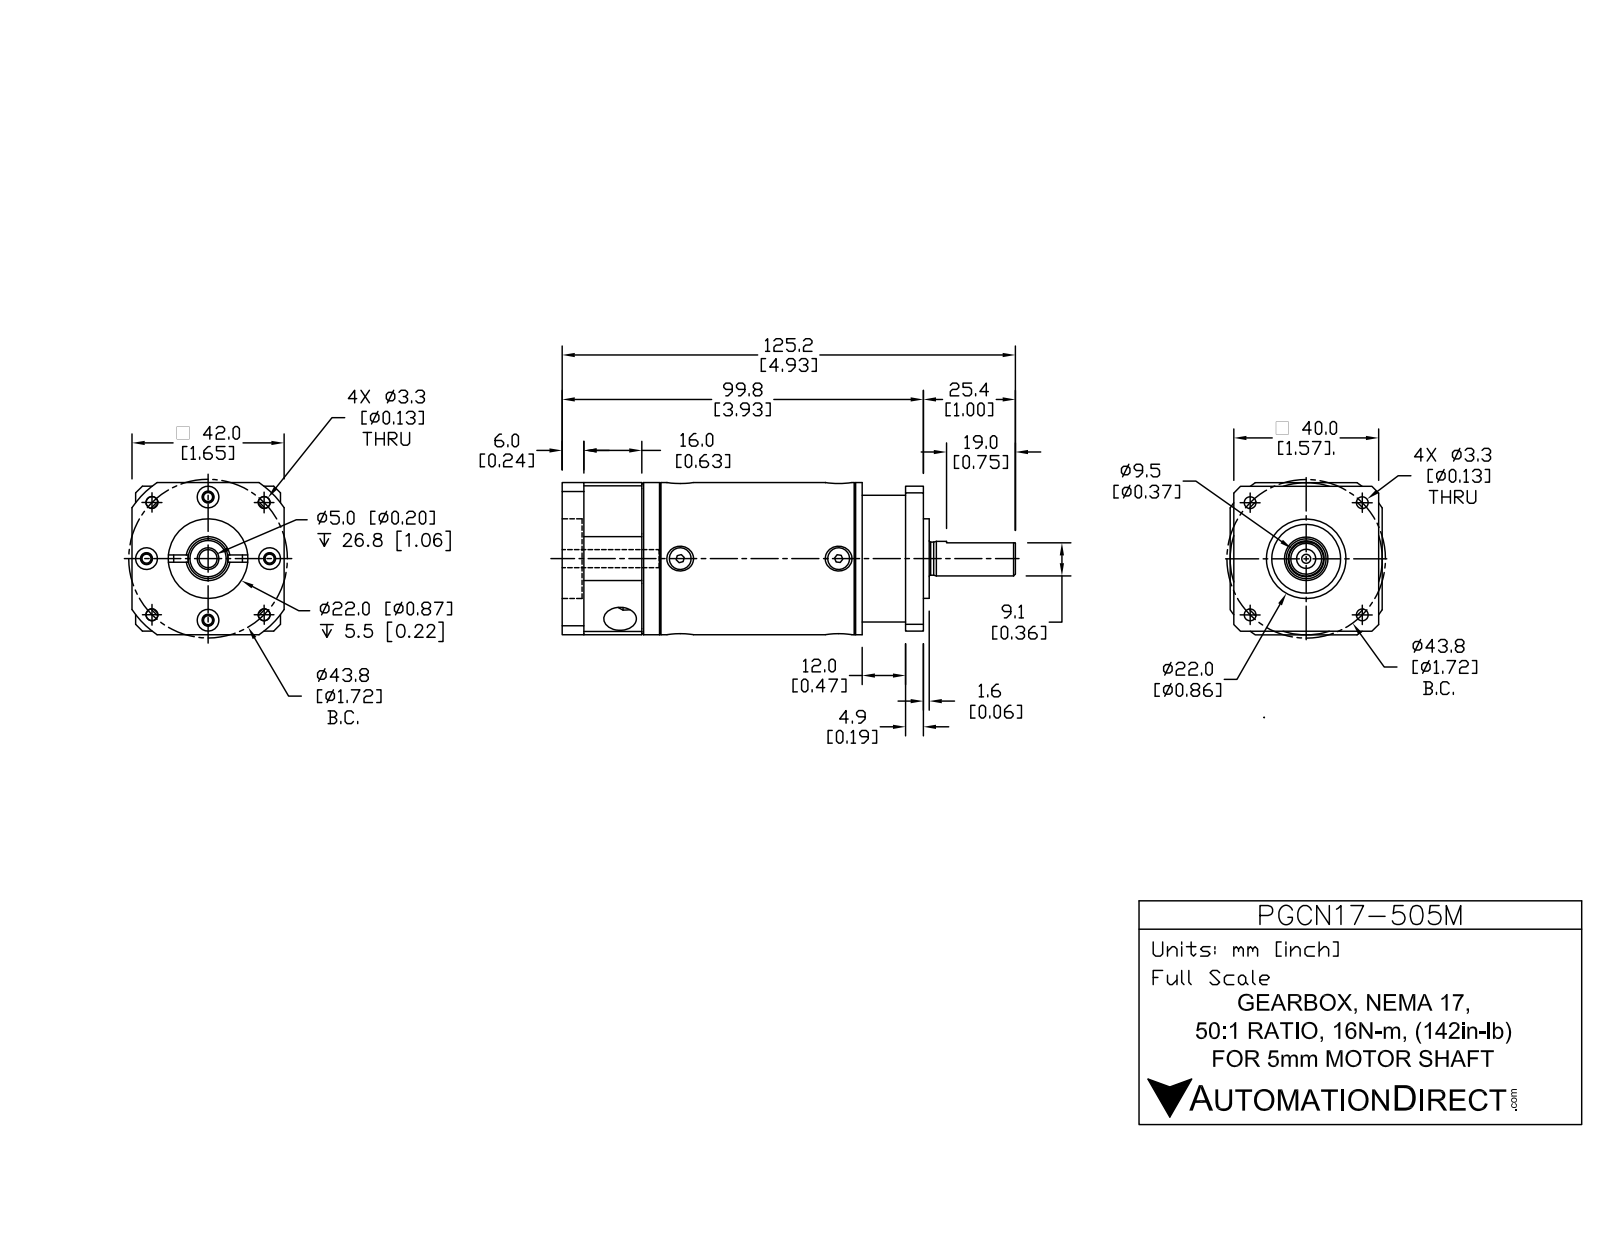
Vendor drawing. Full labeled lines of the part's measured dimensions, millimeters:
Part name (STEP PRODUCT): Bushing_5x11x14.9_1; PE-N17-II 11mm Input; N17-E05_1; PGCN17-505M
STEP written by: SolidWorks 2014 (AUTOMOTIVE_DESIGN)
Units: millimetres
Bodies: 3 solids, 433 faces (137 planar, 174 cylindrical, 122 other)
Overall size (bounding box): 125.1 × 42 × 42
Volume: 123 800 mm³ · Surface area: 29 270 mm²
Round holes (diameter × count): ⌀3.3 ×8, ⌀2.5 ×5, ⌀3 ×4, ⌀3.3 ×4, ⌀3.4 ×4, ⌀6 ×4, ⌀4.5 ×2, ⌀9 ×2, ⌀5 ×1, ⌀11 ×1, ⌀19 ×1, ⌀22 ×1
Round bosses / shafts (diameter × count): ⌀6 ×4, ⌀7 ×2, ⌀4 ×2, ⌀42 ×1, ⌀35 ×1, ⌀22 ×1, ⌀12 ×1, ⌀9.5 ×1
Partial cylindrical surfaces — rounded edges, fillets, slot ends (radius × count): R1.6 ×2, R4 ×2, R19 ×1, R27 ×1, R28 ×1
Main face-to-face distances: 22, 77.7, 99.7, 1, 41, 4.9, 72.8, 94.8, 37, 16
Hole centre spacings: 15.6, 15.6, 31, 36, 36, 17, 21.9, 21.9
